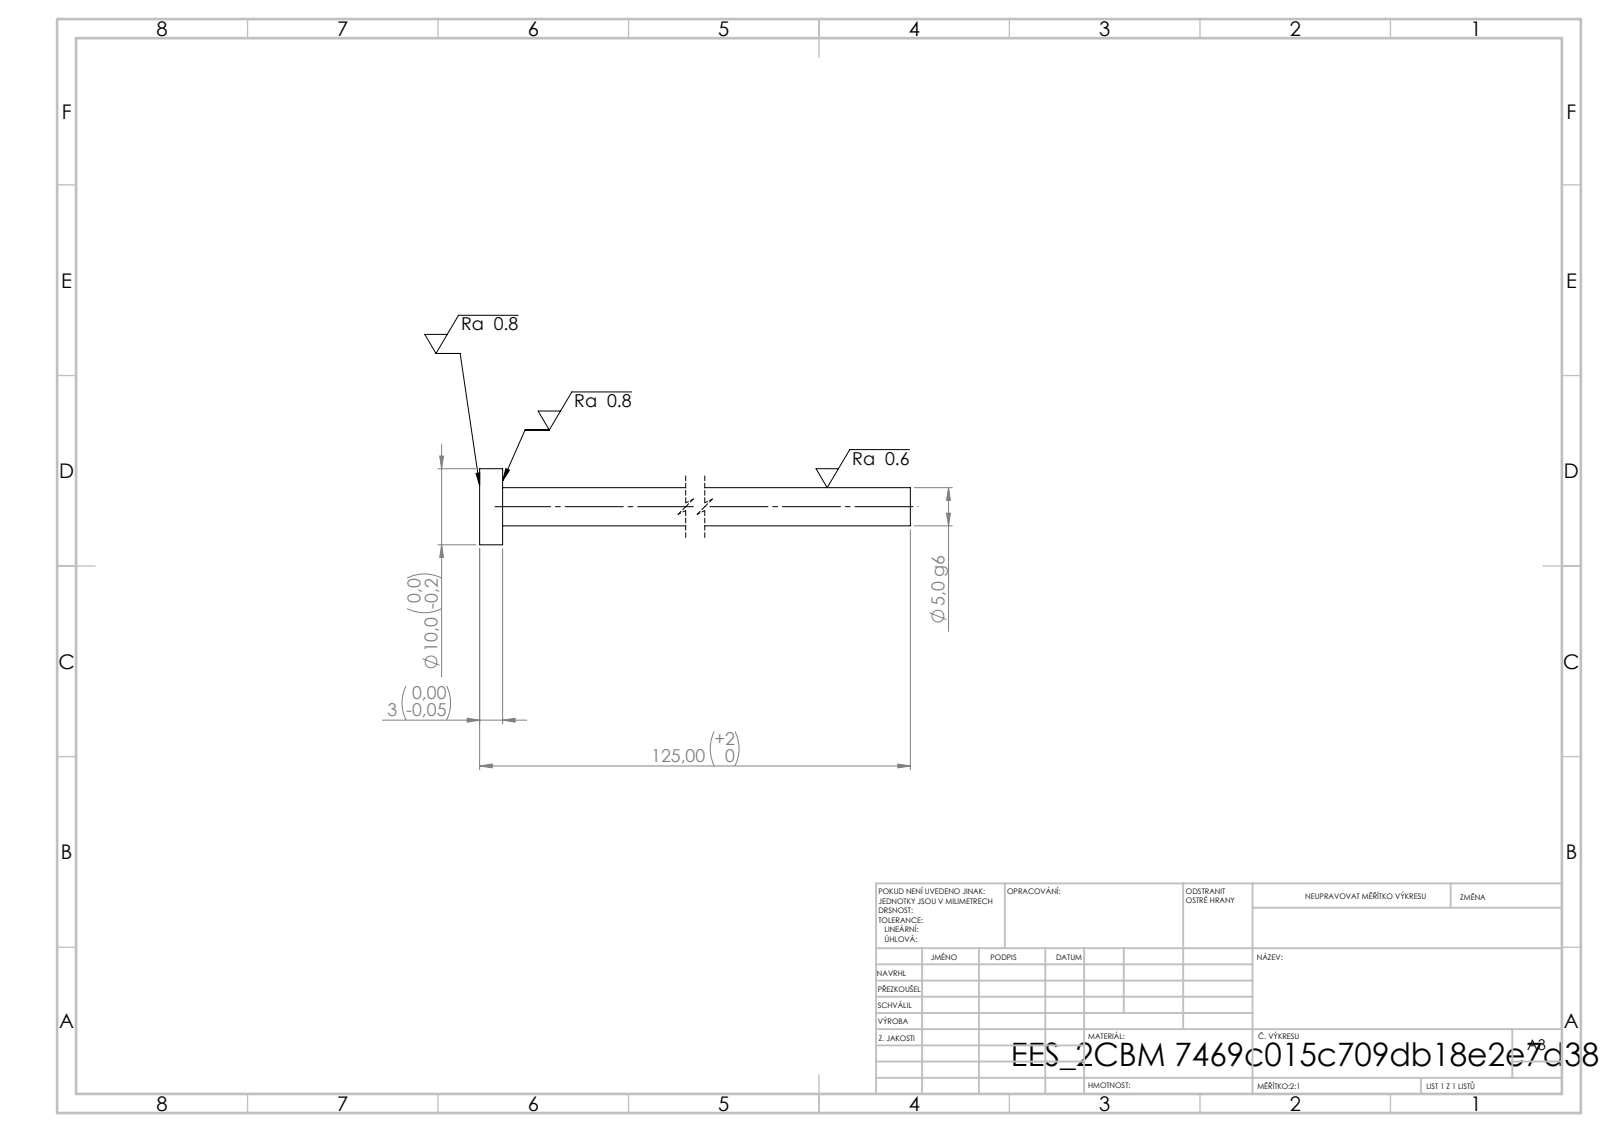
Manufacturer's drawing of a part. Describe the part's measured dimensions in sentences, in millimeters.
Its 3-D file was written by "SolidWorks 2019 (CONFIG_CONTROL_DESIGN)". It is 1 solid with 7 faces: 3 planar, 4 cylindrical and 0 other. Overall it measures 125 by 10 by 10 millimeters. Its volume is 2 631 cubic millimeters and its surface area 2 168 square millimeters. Round bosses or shafts: 1 of diameter 10, 1 of diameter 5. The main face-to-face distances are 3, 125, 122.
